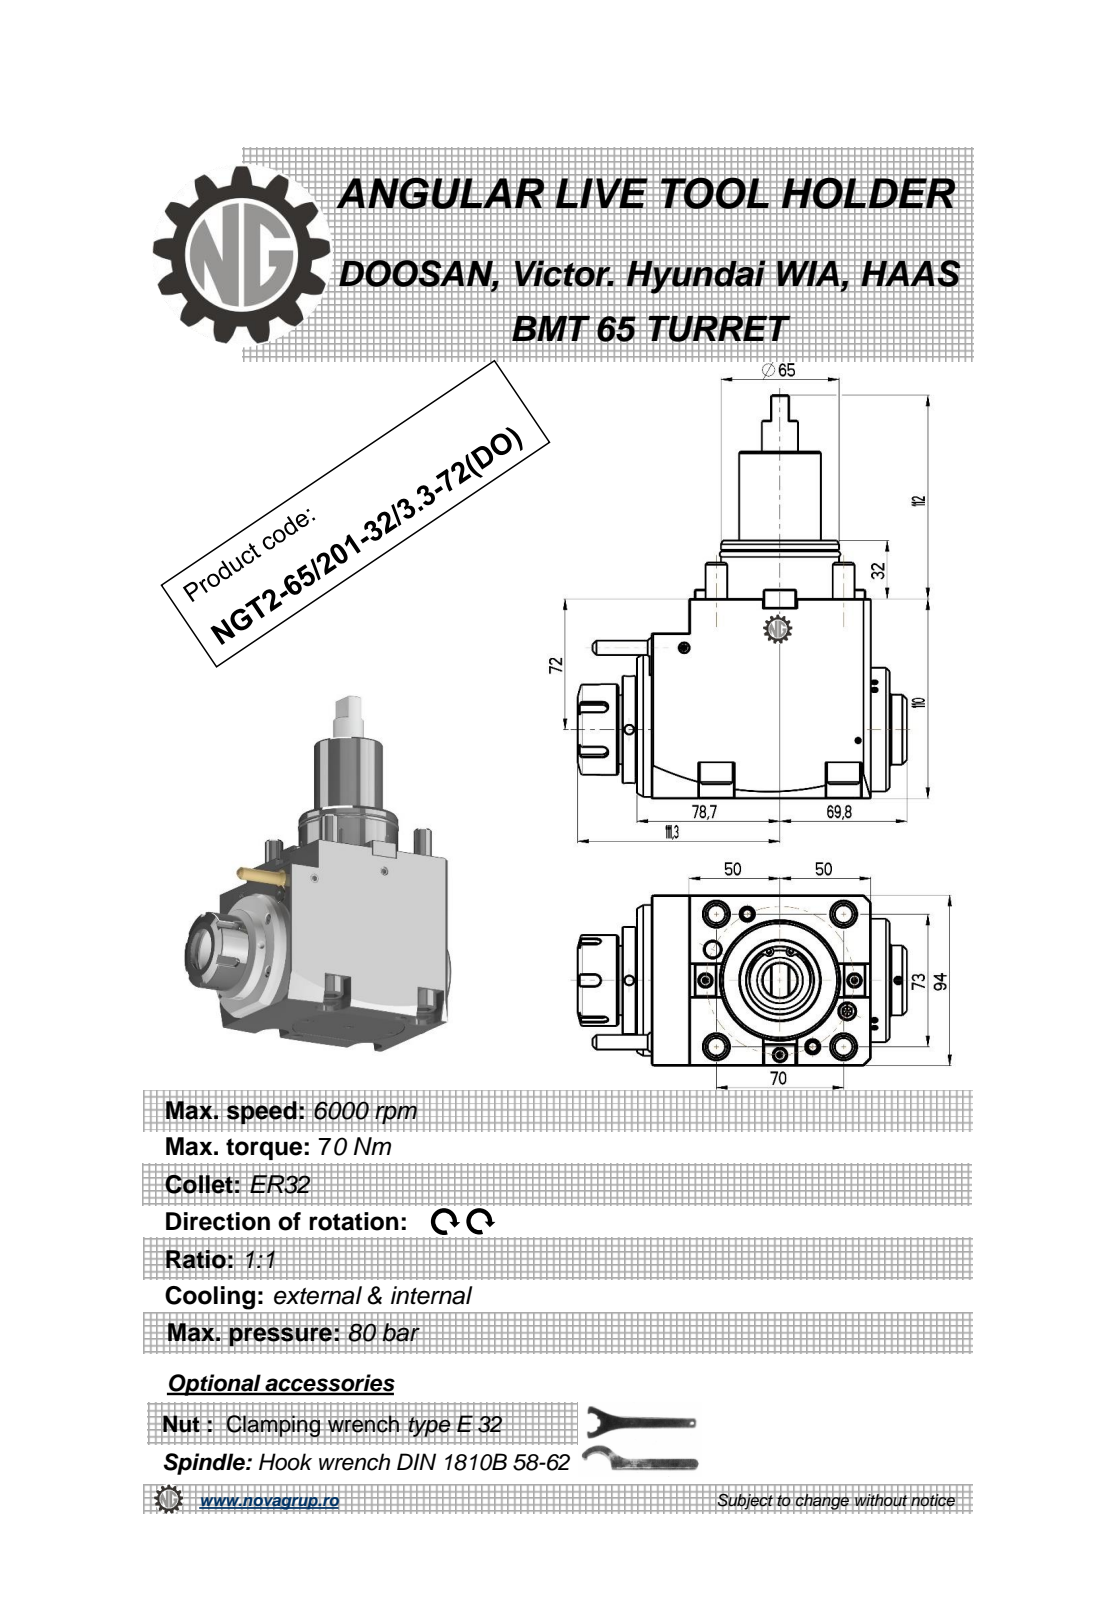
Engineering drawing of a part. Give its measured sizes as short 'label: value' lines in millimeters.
name: NGT2_65_201_32_3_3_72_DO
written by: PRO/ENGINEER BY PARAMETRIC TECHNOLOGY CORPORATION, 2010280 (CONFIG_CONTROL_DESIGN)
unit: mm
bodies: 2 solids, 445 faces (217 planar, 112 cylindrical, 116 other)
size: 222 × 181.1 × 94
volume: 1 544 000 mm³; area: 111 588 mm²
holes: 3× ⌀5, 2× ⌀8.5, 1× ⌀3, 1× ⌀27
bosses: 4× ⌀18, 4× ⌀12, 1× ⌀83, 1× ⌀68, 1× ⌀65, 1× ⌀60, 1× ⌀59, 1× ⌀50
rounds: 20× R0.36, 6× R0.22, 5× R3, 4× R9.5, 2× R0.8, 2× R550
face distances: 94, 110, 8, 128.7, 100, 19, 120.7, 131, 91, 139
hole spacings: 48.99, 56.4, 81.44, 121.15
